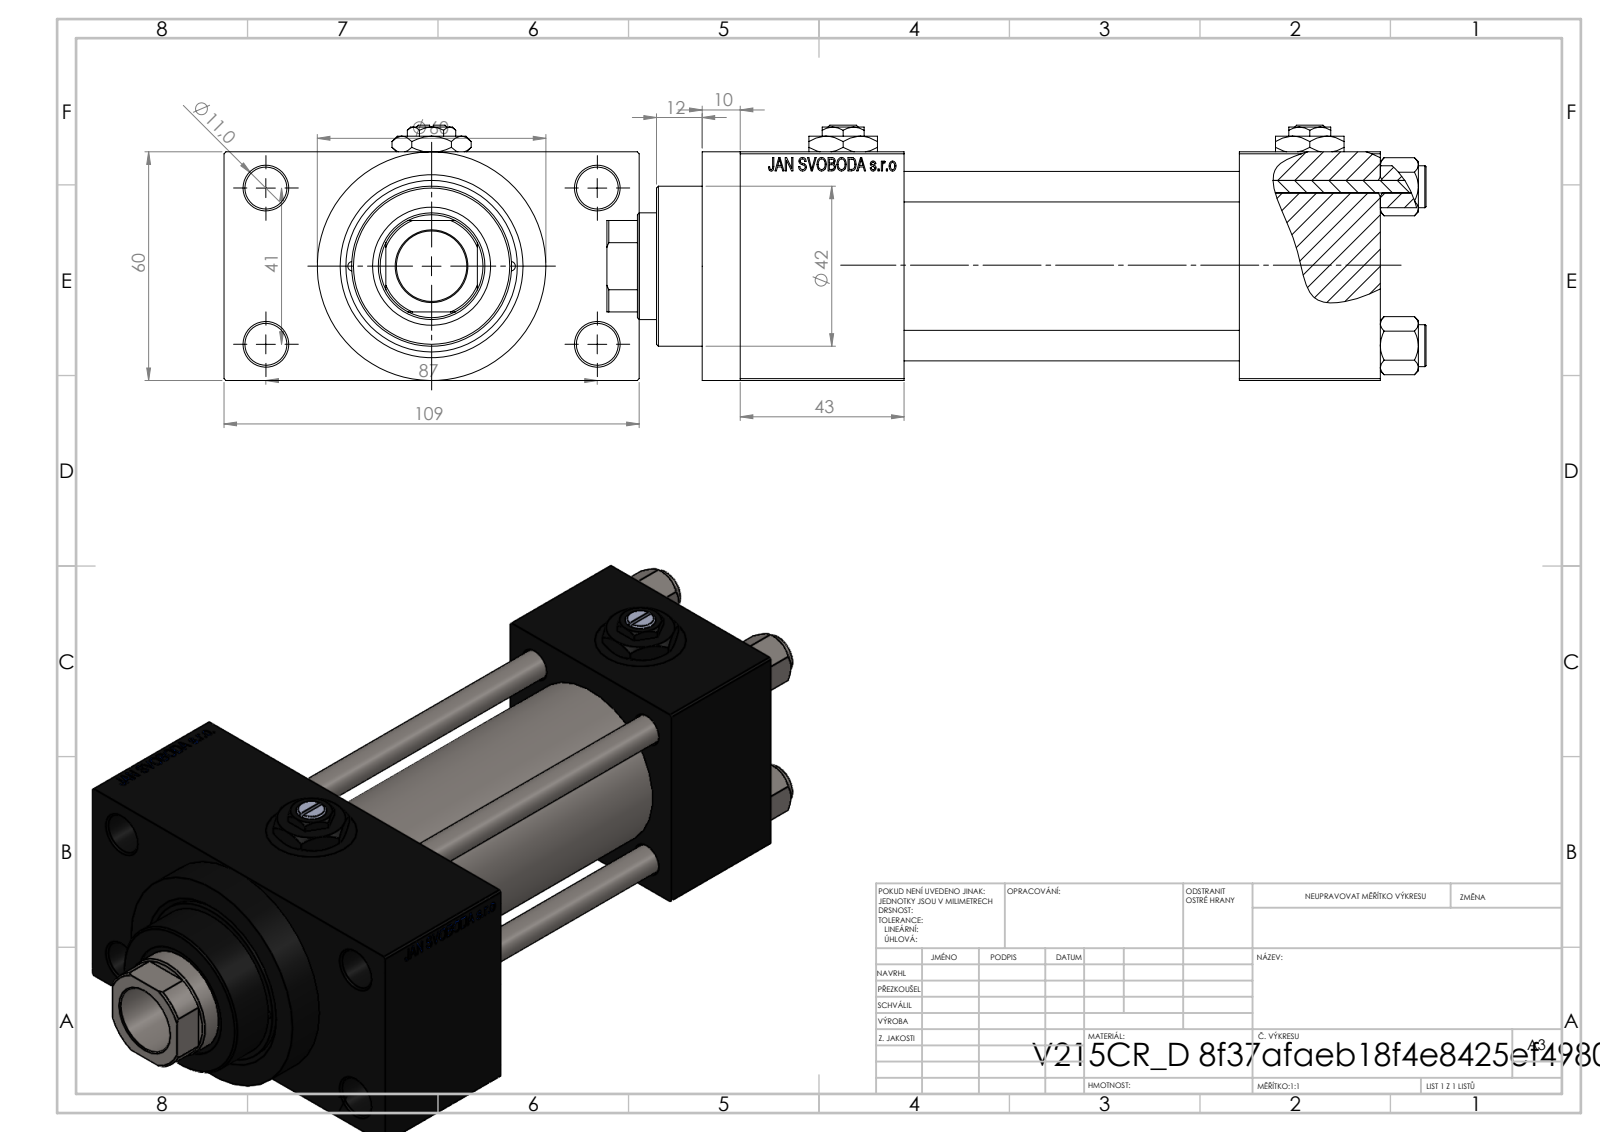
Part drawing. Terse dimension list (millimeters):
name: NUT_M5_D; V215CR_VCP_D; V215CR_D_TYCINKA; V215CR_D_Body (+2 more)
written by: SolidWorks 2019 (CONFIG_CONTROL_DESIGN)
unit: mm
bodies: 13 solids, 1215 faces (550 planar, 103 cylindrical, 562 other)
size: 215 × 109 × 67
volume: 563 142 mm³; area: 145 481 mm²
holes: 4× ⌀8, 4× ⌀11, 4× ⌀16.66, 4× ⌀24, 3× ⌀7, 2× ⌀2.5, 1× ⌀18.5, 1× ⌀28, 1× ⌀31, 1× ⌀40, 1× ⌀45
bosses: 4× ⌀11, 1× ⌀60, 1× ⌀46, 1× ⌀42
rounds: 1× R13.5
face distances: 60, 24.5, 88, 84.5, 37, 125, 168, 131, 43, 109
hole spacings: 20.85, 22.65, 29.49, 30.62, 41.7, 46.53, 47.15, 48.09
